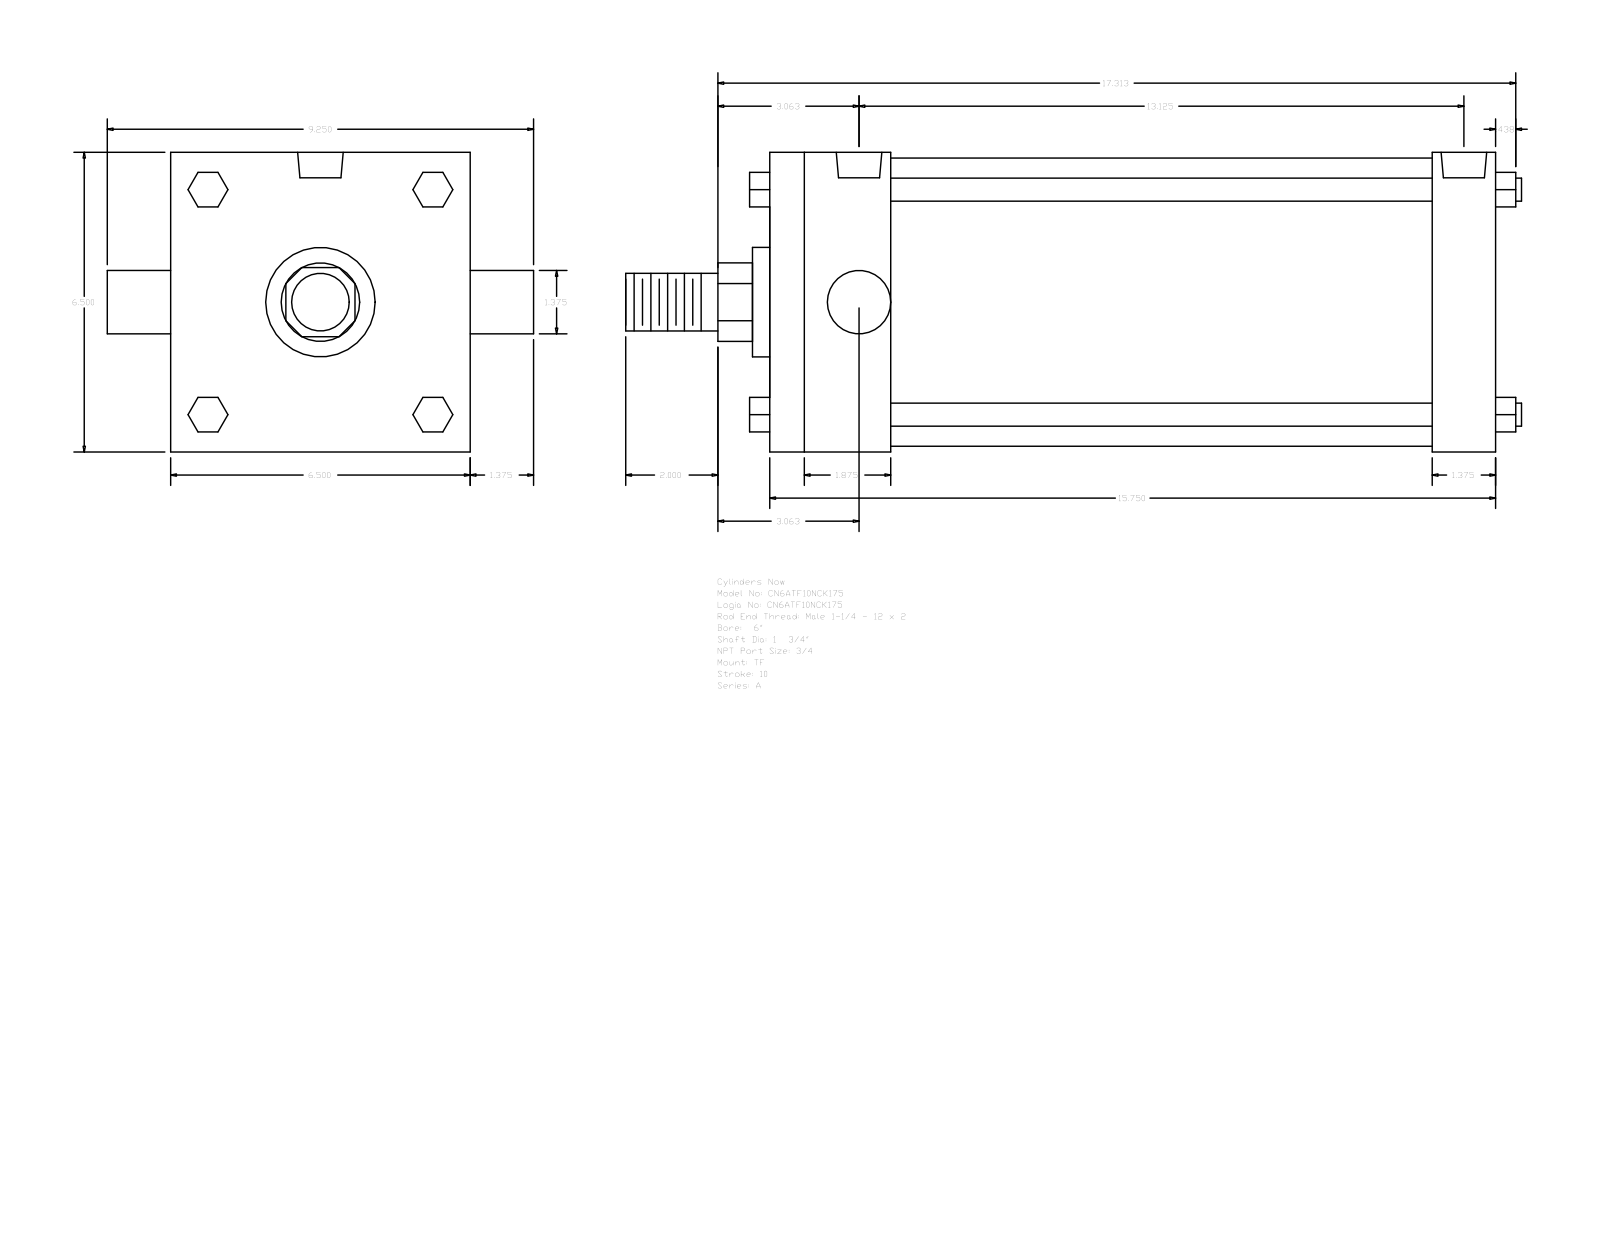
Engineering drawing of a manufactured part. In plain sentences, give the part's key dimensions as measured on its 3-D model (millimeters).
The part is named "A_TF__0600_1.75". Its 3-D file was written by "GSSL Pune (CONFIG_CONTROL_DESIGN)". It is 0 solids with 120 faces: 92 planar, 28 cylindrical and 0 other. Overall it measures 493.71 by 234.95 by 165.1 millimeters. Round holes: 3 of diameter 15.08, 2 of diameter 25.12. Round bosses or shafts: 4 of diameter 12.7, 1 of diameter 158.75, 1 of diameter 60.33, 1 of diameter 44.45, 1 of diameter 34.92, 1 of diameter 31.75. Partial cylindrical surfaces (rounded edges, fillets, slot ends): 1 of radius 21.63. The main face-to-face distances are 165.1, 400.05, 34.92, 66.68, 333.37, 365.13, 298.45, 19.05, 61.97, 107.34. The hole center spacings are 5.56, 327.81, 322.25, 333.37.
